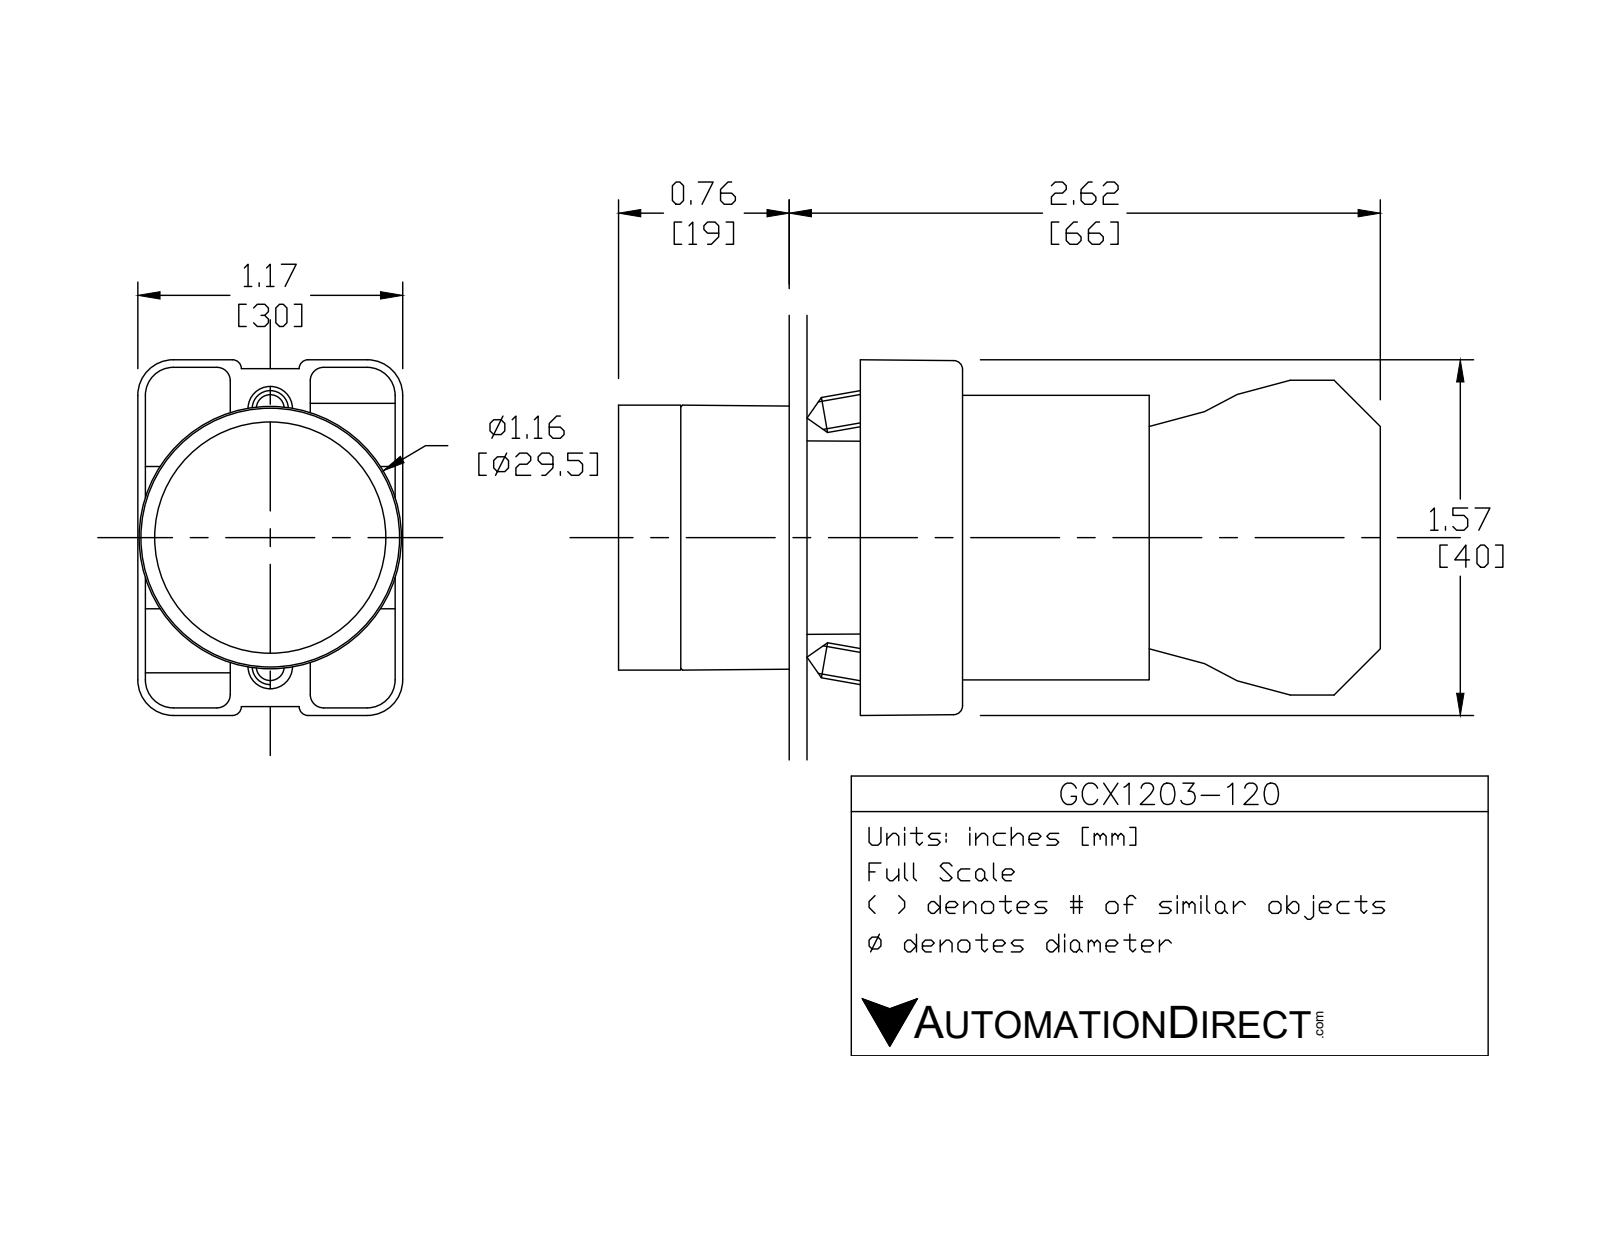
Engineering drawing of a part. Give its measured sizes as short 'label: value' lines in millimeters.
name: GCX1203-120; ecx1040; ecx1029; GCX1203 OPERATOR (+1 more)
written by: SolidWorks 2016 (AUTOMOTIVE_DESIGN)
unit: mm
bodies: 8 solids, 431 faces (252 planar, 148 cylindrical, 31 other)
size: 84.3 × 40.2 × 29.9
volume: 45 790 mm³; area: 25 000 mm²
holes: 2× ⌀2, 2× ⌀3.1, 2× ⌀3.3, 1× ⌀2.2, 1× ⌀5, 1× ⌀11.9, 1× ⌀22.3, 1× ⌀22.6, 1× ⌀26
bosses: 4× ⌀4, 1× ⌀29.8, 1× ⌀25.5, 1× ⌀24, 1× ⌀21.7, 1× ⌀19.8, 1× ⌀12.8
rounds: 24× R1.5, 12× R1, 12× R3.1, 12× R4, 8× R1, 2× R3.3, 1× R0.5, 1× R1.6
face distances: 21, 51.3, 30.3, 14.7, 29.7, 0.8, 7, 0.8, 19, 14.6
hole spacings: 6, 13.8, 12, 12.4
